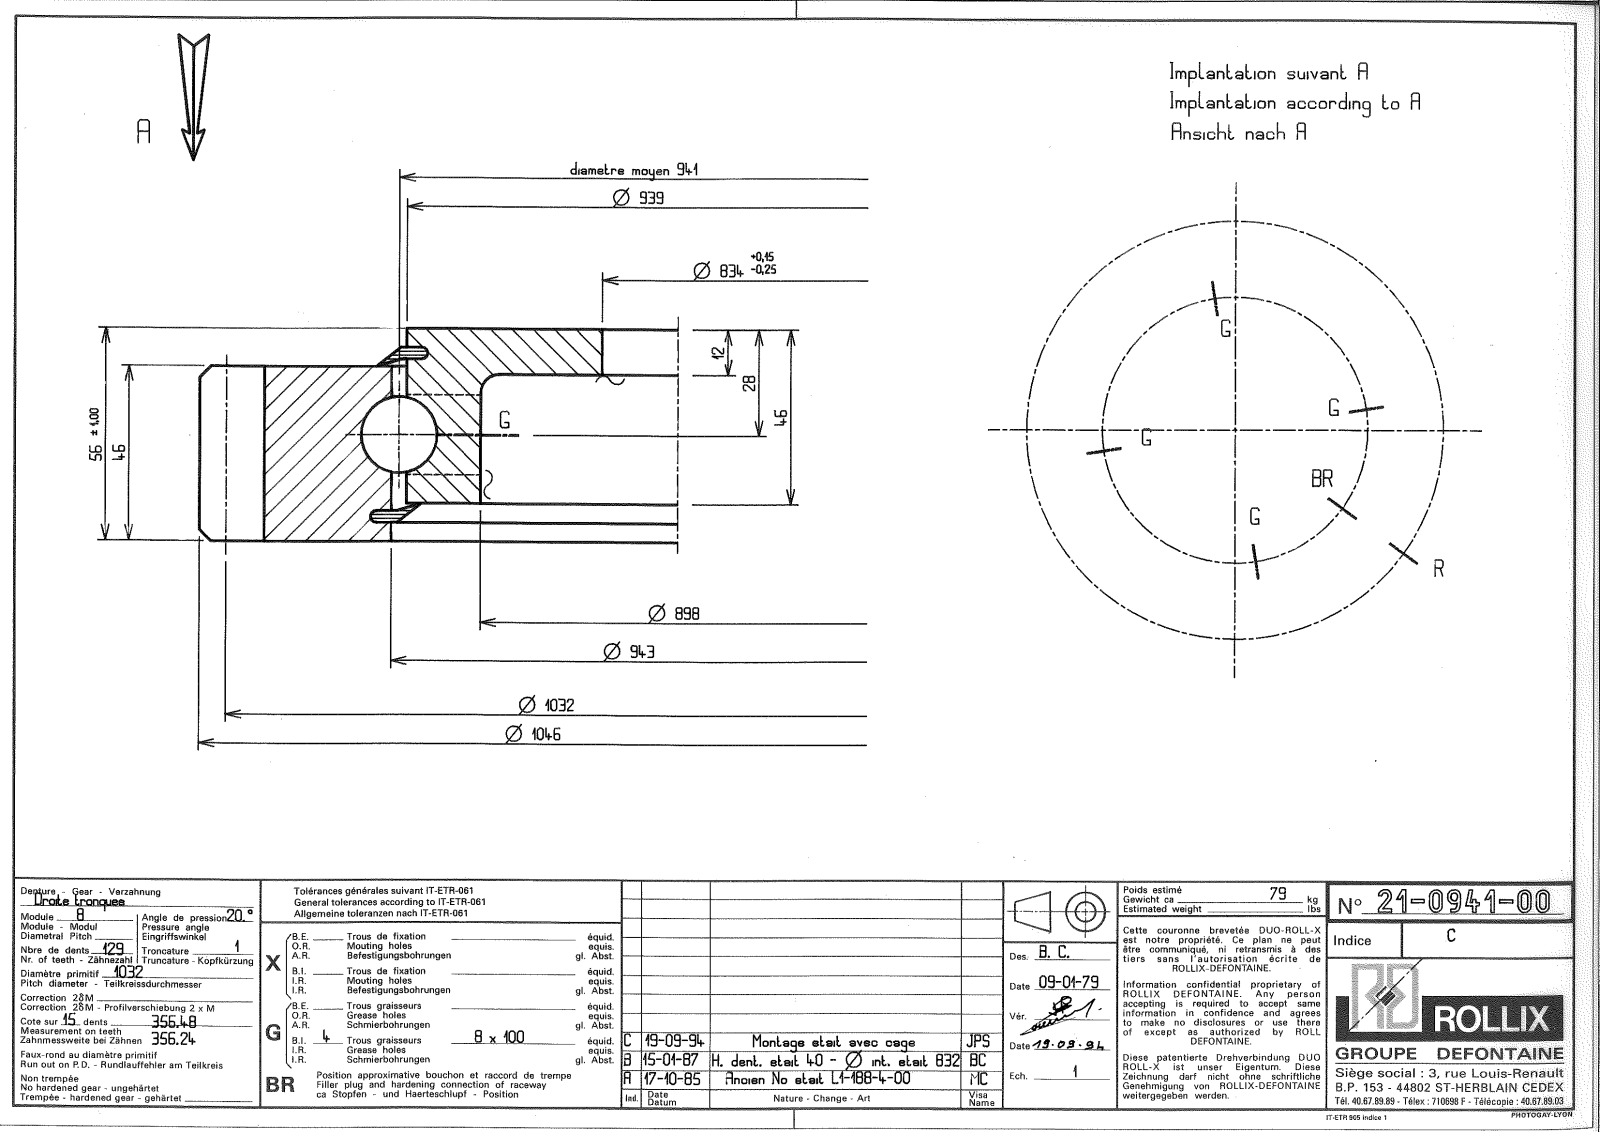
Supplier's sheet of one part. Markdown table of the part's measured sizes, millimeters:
| quantity | value |
| --- | --- |
| part name | 21-0941-00 |
| STEP written by | SolidWorks 2016 (CONFIG_CONTROL_DESIGN) |
| units | millimeters |
| bodies | 9 solids, 931 faces (311 planar, 291 cylindrical, 329 other) |
| overall size | 1045.99 × 1045.93 × 56 |
| volume | 9 145 000 mm³ |
| surface area | 1 503 000 mm² |
| round holes (diameter × count) | 7 × 2, 834 × 1, 898 × 1, 945.5 × 1 |
| round bosses / shafts (diameter × count) | 8 × 2, 936.5 × 1 |
| partial cylindrical surfaces (radius × count) | 506 × 1, 523 × 1 |
| main face-to-face distances | 10, 46, 56, 44, 2, 12, 34, 36, 8.05, 47.95 |
